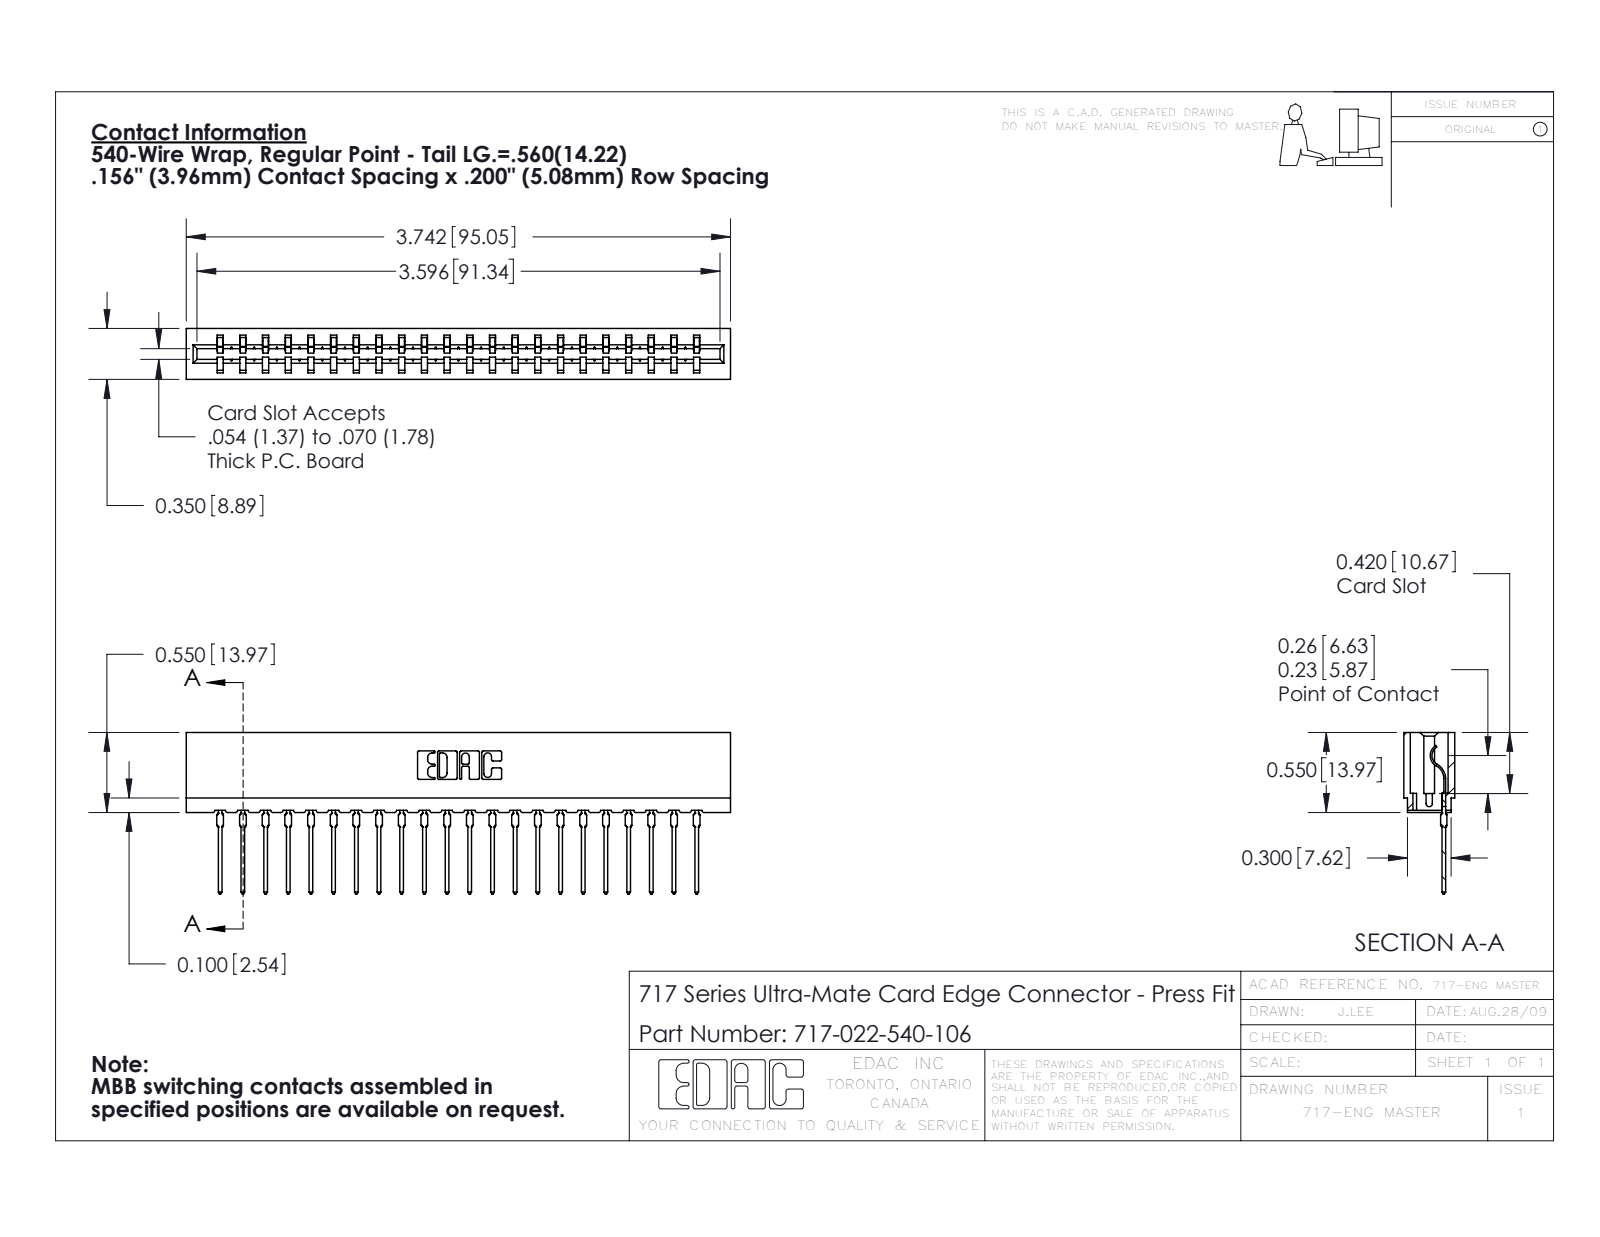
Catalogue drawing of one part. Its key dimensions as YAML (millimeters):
part_name: "745-292-001_540; 717 Part_Insulator Option - 06; 717-022-540-106"
step_written_by: "SolidWorks 2016 (CONFIG_CONTROL_DESIGN)"
units: millimeters
bodies: {solids: 23, faces: 2580, planar: 1550, cylindrical: 458, other: 572}
overall_size: [95, 28.2, 8.9]
volume: 8160
surface_area: 11510
partial_cylinders:
  - {radius: 0.4, count: 44}
  - {radius: 0.5, count: 44}
  - {radius: 0.3, count: 22}
  - {radius: 0.2, count: 6}
  - {radius: 0.8, count: 6}
  - {radius: 0.1, count: 4}
  - {radius: 0.3, count: 4}
  - {radius: 0.7, count: 3}
face_to_face_distances: [5.4, 3.5, 8.9, 4, 1.9, 1.6, 7.3, 1.9, 3.8, 15.8]
